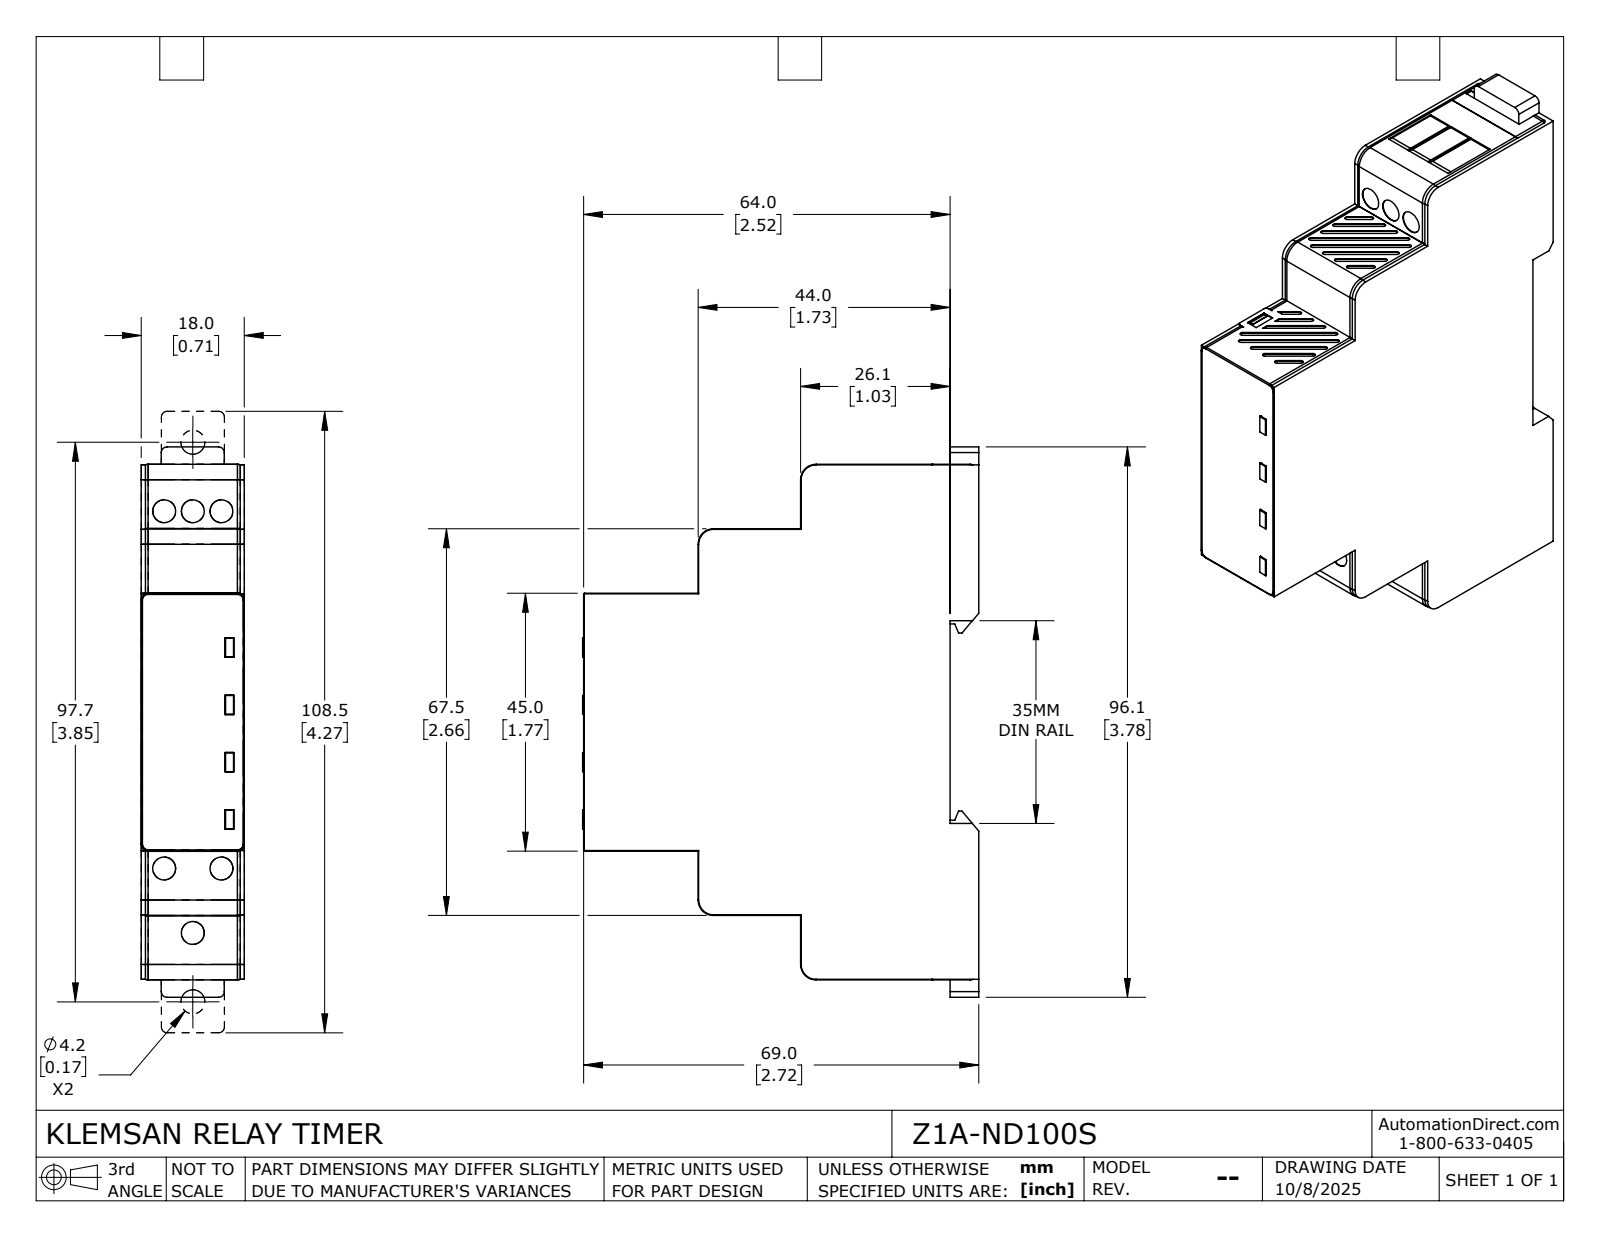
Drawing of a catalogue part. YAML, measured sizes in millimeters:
part_name: "Z1A-ND100S"
step_written_by: "SolidWorks 2024 (CONFIG_CONTROL_DESIGN)"
units: millimeters
bodies: {solids: 3, faces: 440, planar: 280, cylindrical: 60, other: 100}
overall_size: [96.07, 69.15, 18]
volume: 83847
surface_area: 17884
round_holes:
  - {diameter: 4.2, count: 2}
  - {diameter: 4, count: 1}
partial_cylinders:
  - {radius: 1.2, count: 16}
  - {radius: 0.2, count: 4}
  - {radius: 1, count: 4}
  - {radius: 2.6, count: 4}
  - {radius: 2.7, count: 4}
  - {radius: 0.5, count: 2}
  - {radius: 1.5, count: 2}
face_to_face_distances: [18, 3.5, 14.5, 11.25, 64, 5, 69, 22.5, 67.4, 67.5]
hole_center_spacings: [5.83, 79.43, 85.26]
